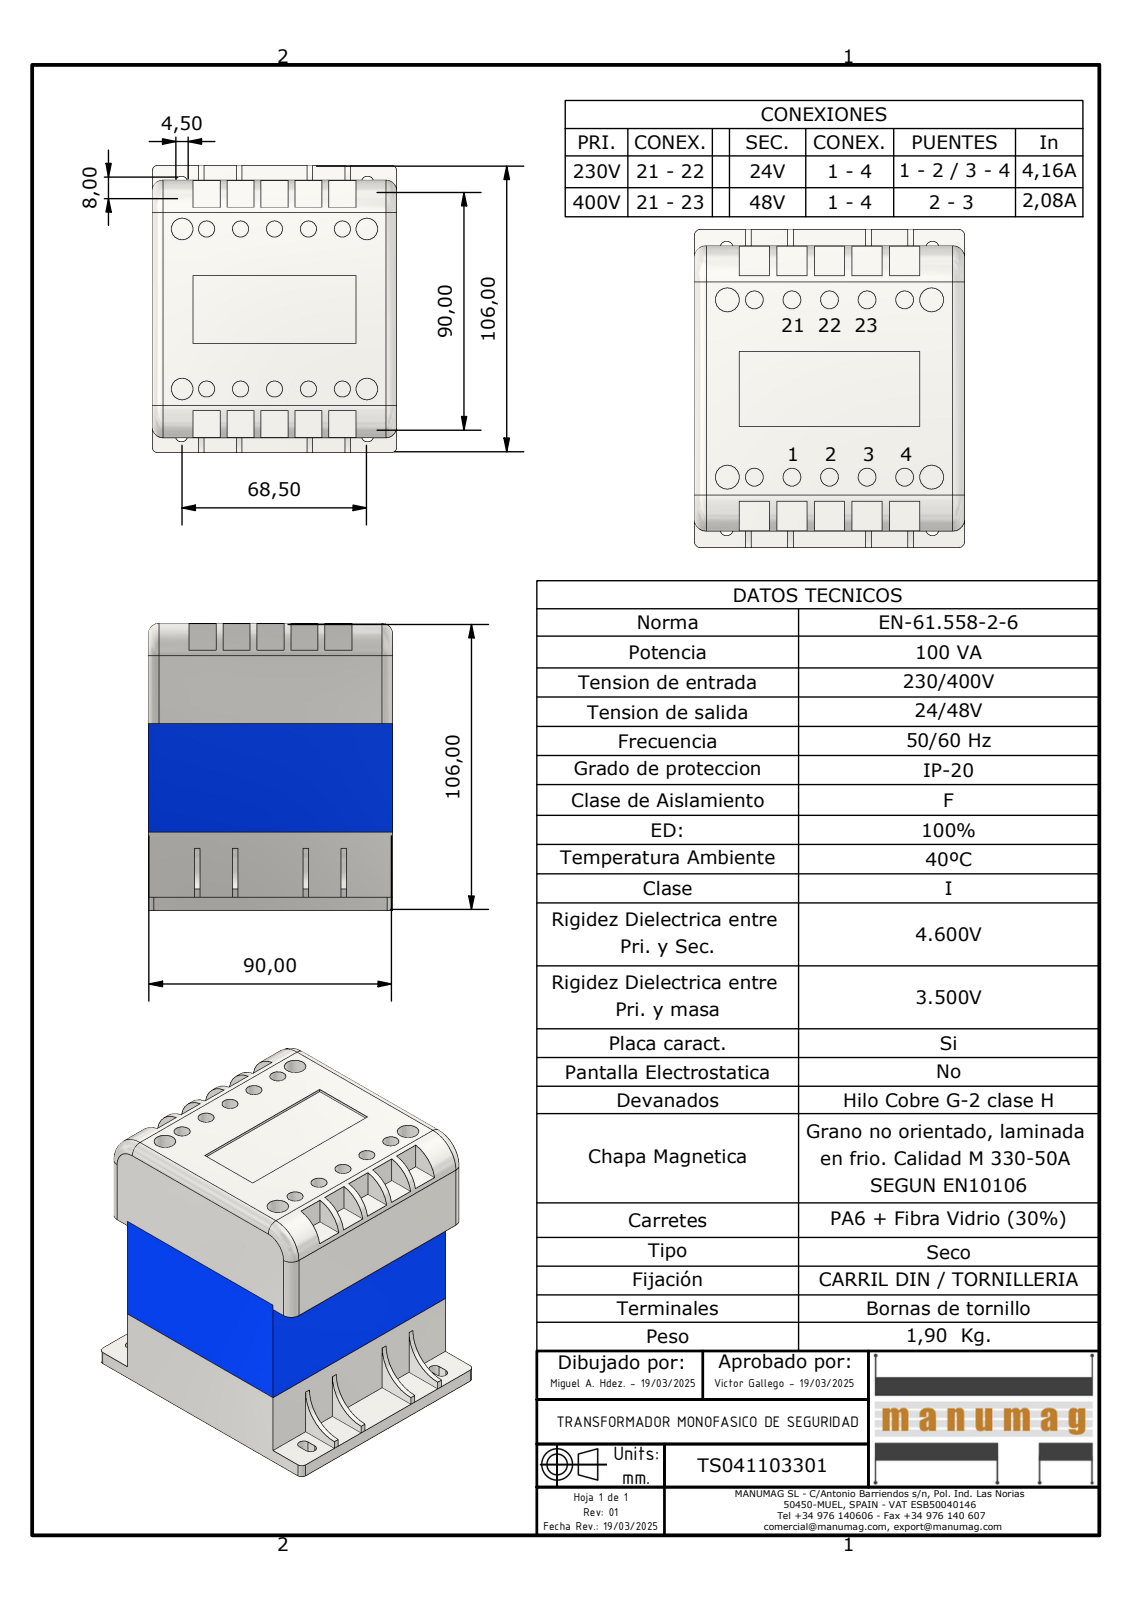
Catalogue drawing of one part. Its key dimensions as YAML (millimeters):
part_name: "TS041103301; CENTRAL EI84-40; SUPERIOR EI84; INFERIOR EI84"
step_written_by: "Autodesk Inventor 2023 (AUTOMOTIVE_DESIGN)"
units: millimeters
bodies: {solids: 11, faces: 188, planar: 142, cylindrical: 42, other: 4}
overall_size: [106, 106, 90]
volume: 352957
surface_area: 101743
round_holes:
  - {diameter: 6, count: 10}
  - {diameter: 8, count: 4}
partial_cylinders:
  - {radius: 2.25, count: 8}
  - {radius: 4, count: 6}
  - {radius: 2, count: 4}
  - {radius: 12, count: 2}
  - {radius: 15, count: 2}
face_to_face_distances: [1, 75, 89, 5, 90, 71, 66, 76, 74, 88]
hole_center_spacings: [59, 12.5, 60.31, 25, 64.08, 9, 21.5, 34]
